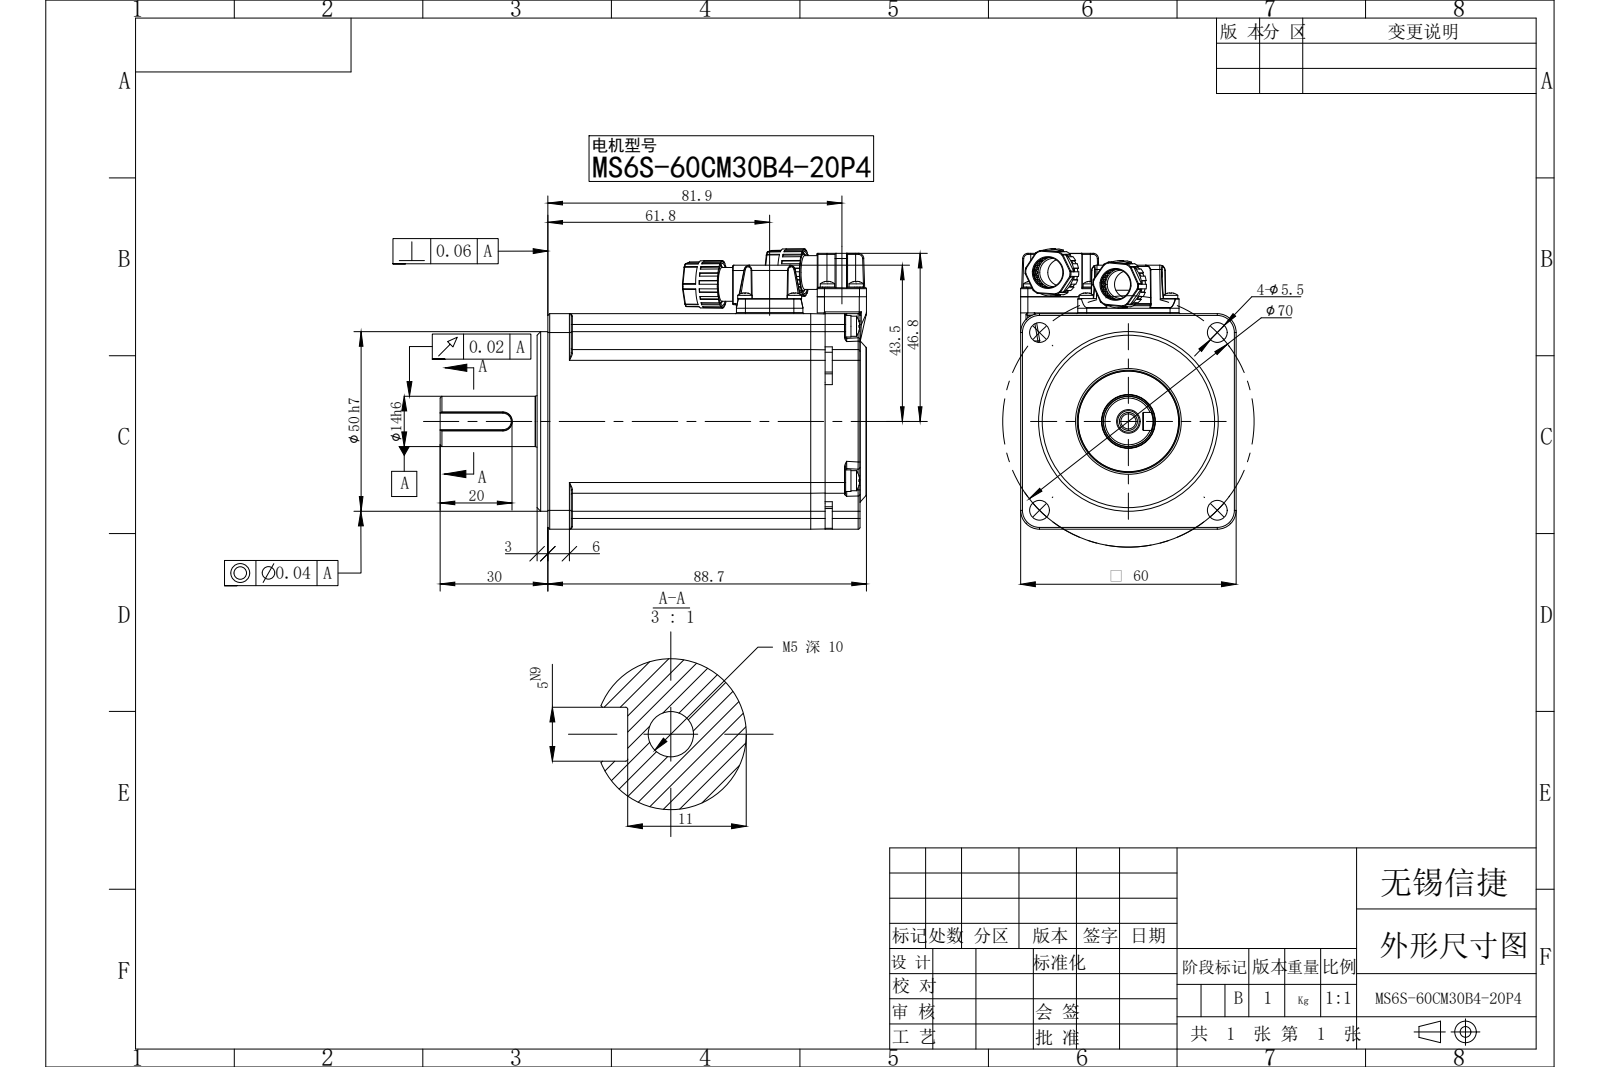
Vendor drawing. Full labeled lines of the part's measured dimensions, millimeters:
Part name (STEP PRODUCT): MS6S-60CM30B4-20P4
STEP written by: SolidWorks 2022 (CONFIG_CONTROL_DESIGN)
Units: millimetres
Bodies: 0 solids, 1116 faces (435 planar, 387 cylindrical, 294 other)
Overall size (bounding box): 118.7 × 78.06 × 60
Round holes (diameter × count): ⌀5.5 ×4, ⌀11.5 ×2, ⌀11.7 ×2, ⌀4.2 ×1, ⌀5 ×1, ⌀10.4 ×1, ⌀15 ×1
Round bosses / shafts (diameter × count): ⌀4 ×8, ⌀6 ×4, ⌀5.6 ×4, ⌀5.5 ×4, ⌀9.4 ×2, ⌀50 ×1, ⌀28 ×1, ⌀14 ×1
Partial cylindrical surfaces — rounded edges, fillets, slot ends (radius × count): R0.5 ×51, R0.3 ×37, R0.35 ×20, R0.2 ×17, R3 ×17, R1.5 ×13, R2 ×10, R0.15 ×7
Main face-to-face distances: 60, 11.5, 80.2, 3, 91.7, 77.2, 88.7, 89.9, 86.9, 9.7
Hole centre spacings: 35, 49.5, 23.57, 70, 23.55, 23.56
